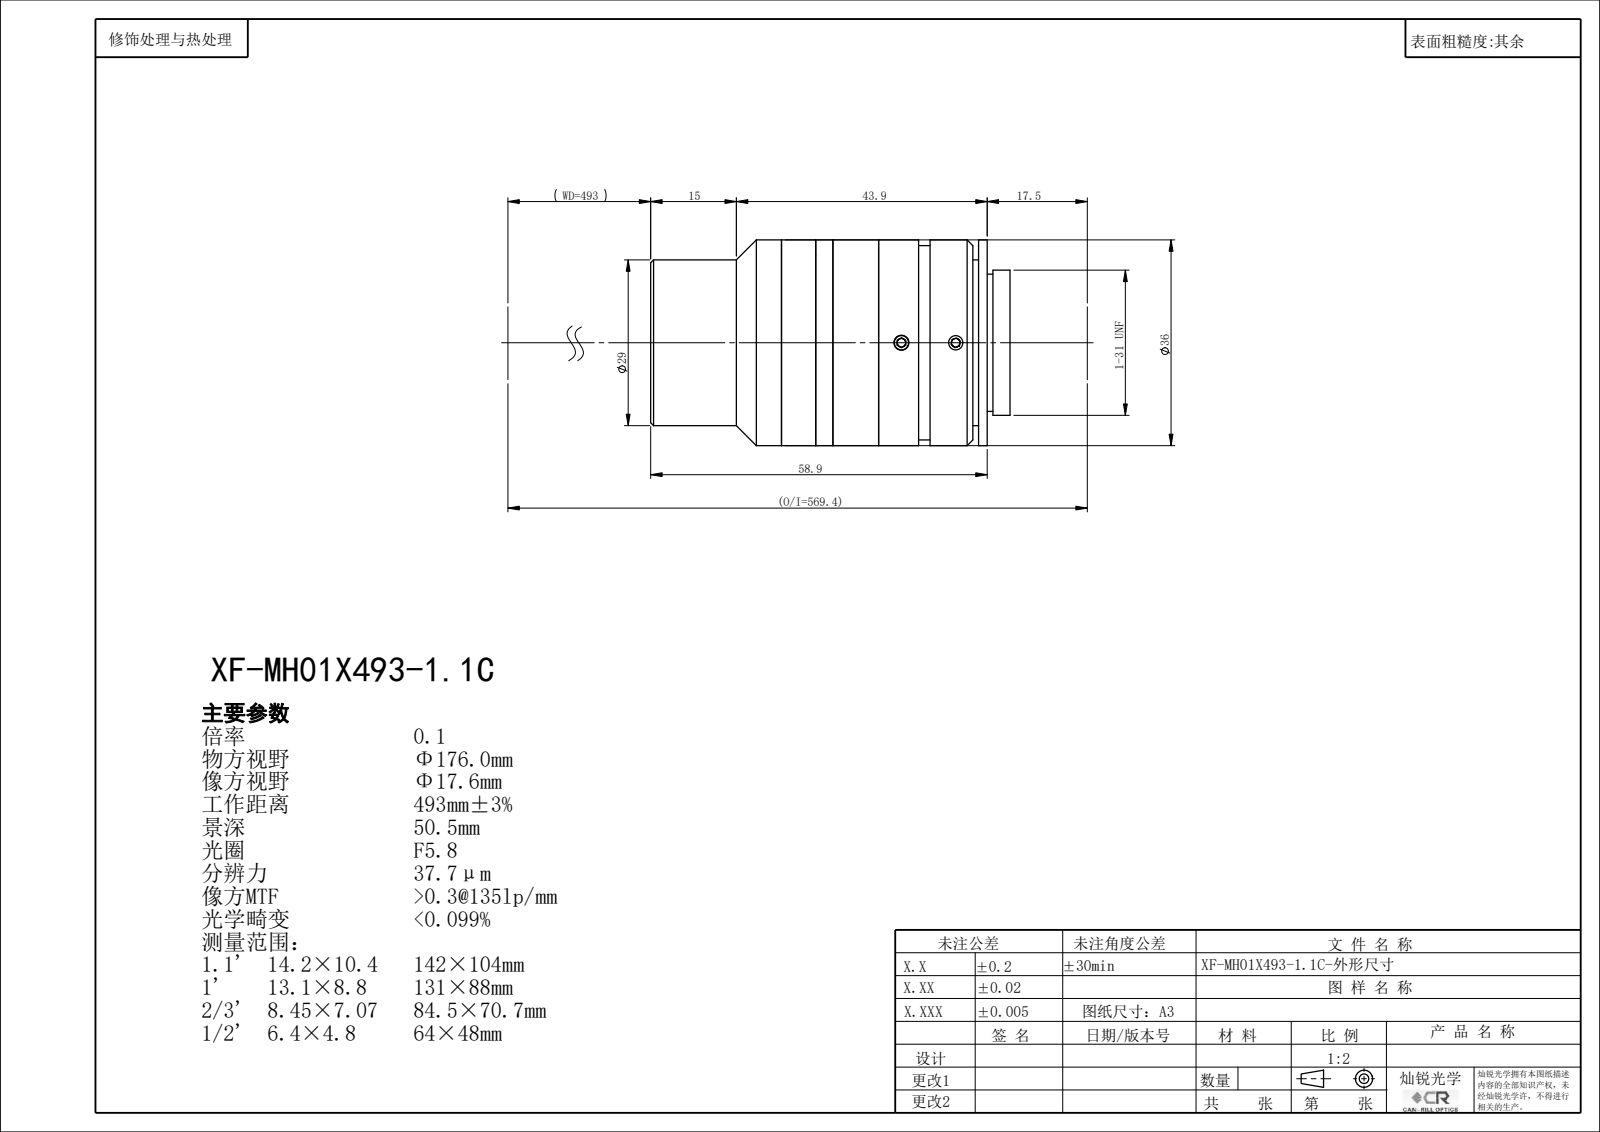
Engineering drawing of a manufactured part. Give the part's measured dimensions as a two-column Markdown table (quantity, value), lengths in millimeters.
| quantity | value |
| --- | --- |
| part name | XF-MH01X493-1.1C |
| STEP written by | SolidWorks 2022 (CONFIG_CONTROL_DESIGN) |
| units | millimeters |
| bodies | 0 solids, 139 faces (68 planar, 42 cylindrical, 29 other) |
| overall size | 62.9 × 36 × 36 |
| round holes (diameter × count) | 2.5 × 3, 20 × 1, 22.4 × 1, 24 × 1, 24.9 × 1, 26 × 1, 26.4 × 1 |
| round bosses / shafts (diameter × count) | 36 × 1, 34 × 1, 29 × 1, 25.4 × 1 |
| main face-to-face distances | 19, 14, 1.5, 1, 10.5, 17.5, 8, 25.5, 27, 6 |
